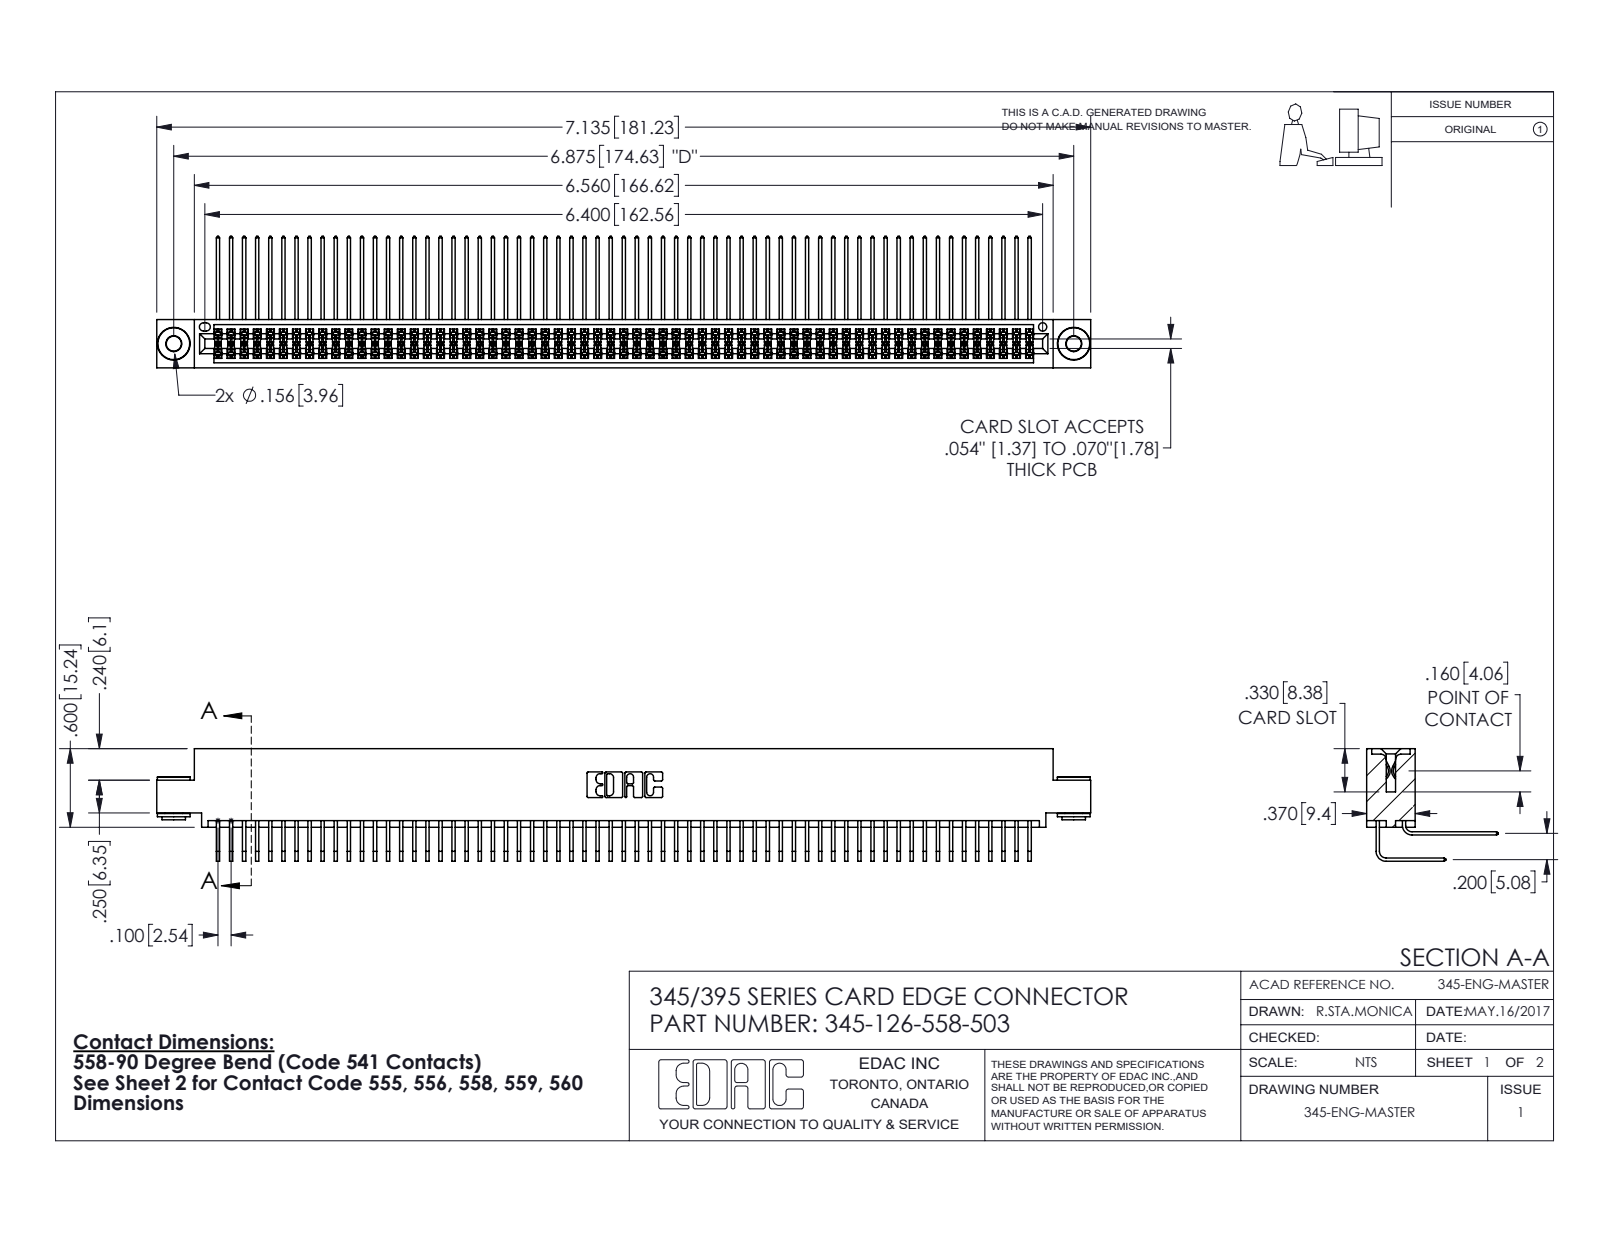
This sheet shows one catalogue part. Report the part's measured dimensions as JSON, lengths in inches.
{"part_name": "345-292-001_558 559 Tail - 1; 345-250-002_345-250-002-102; 345-292-001_558 Tail - 2; 345 Part_0.110 Offset - 0.156 Dia-TH (+1 more)", "step_written_by": "SolidWorks 2016 (CONFIG_CONTROL_DESIGN)", "units": "inches", "bodies": {"solids": 129, "faces": 6720, "planar": 4504, "cylindrical": 2208, "other": 8}, "overall_size": [7.135, 1.005, 0.859], "volume_in3": 1.127, "surface_area_in2": 48.71, "round_holes": [[0.116, 2], [0.156, 2], [0.064, 1]], "round_bosses_or_shafts": [[0.25, 2], [0.18, 2], [0.136, 2]], "partial_cylinders_radius": [[0.006, 252], [0.01, 22], [0.007, 6], [0.031, 6], [0.026, 3], [0.014, 2], [0.019, 2], [0.022, 2]], "face_to_face_distances": [0.072, 0.298, 0.2, 0.025, 0.37, 0.098, 0.272, 0.225, 0.025, 0.175], "hole_center_spacings": [0.27, 6.639, 6.875]}
